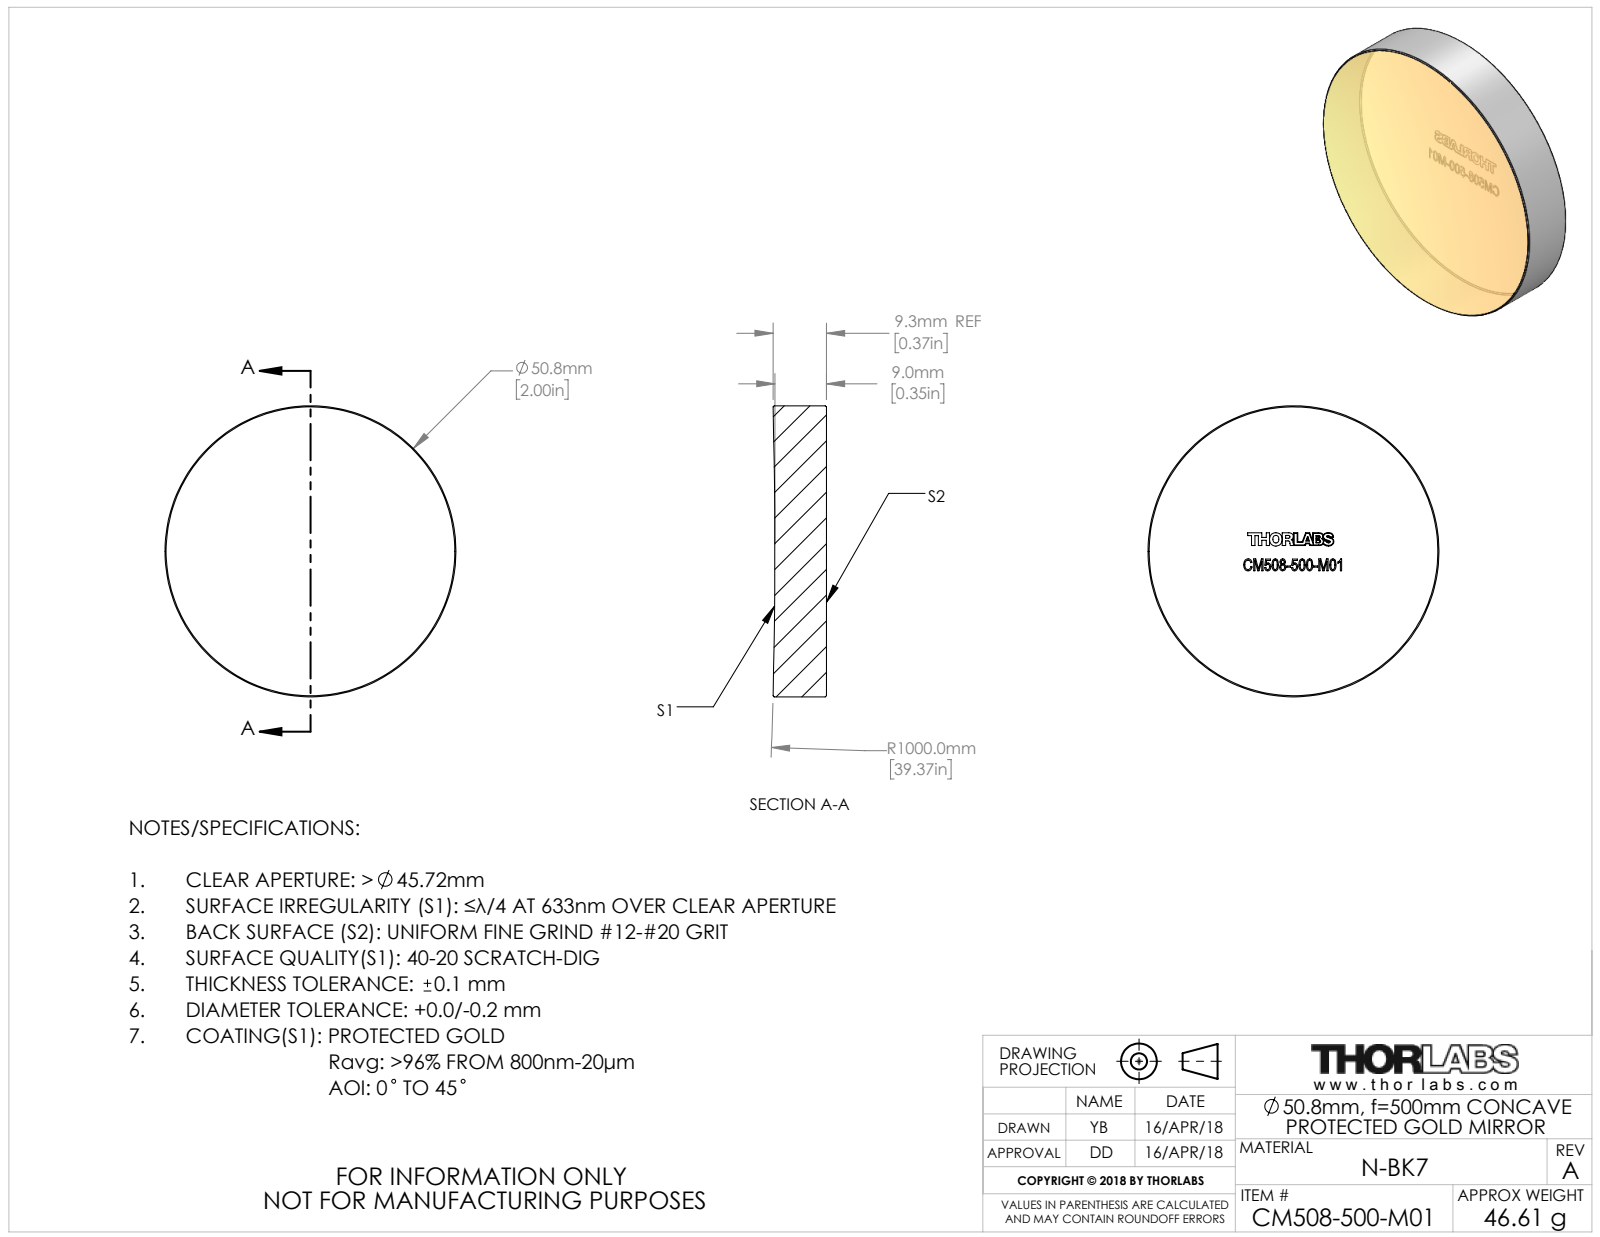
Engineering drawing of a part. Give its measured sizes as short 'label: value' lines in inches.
name: TTN153324-E0W
written by: SolidWorks 2018 (CONFIG_CONTROL_DESIGN)
unit: in
bodies: 1 solid, 43 faces (35 planar, 2 cylindrical, 6 other)
size: 2 × 2 × 0.367
volume: 1.133 in³; area: 8.531 in²
bosses: 1× ⌀2
